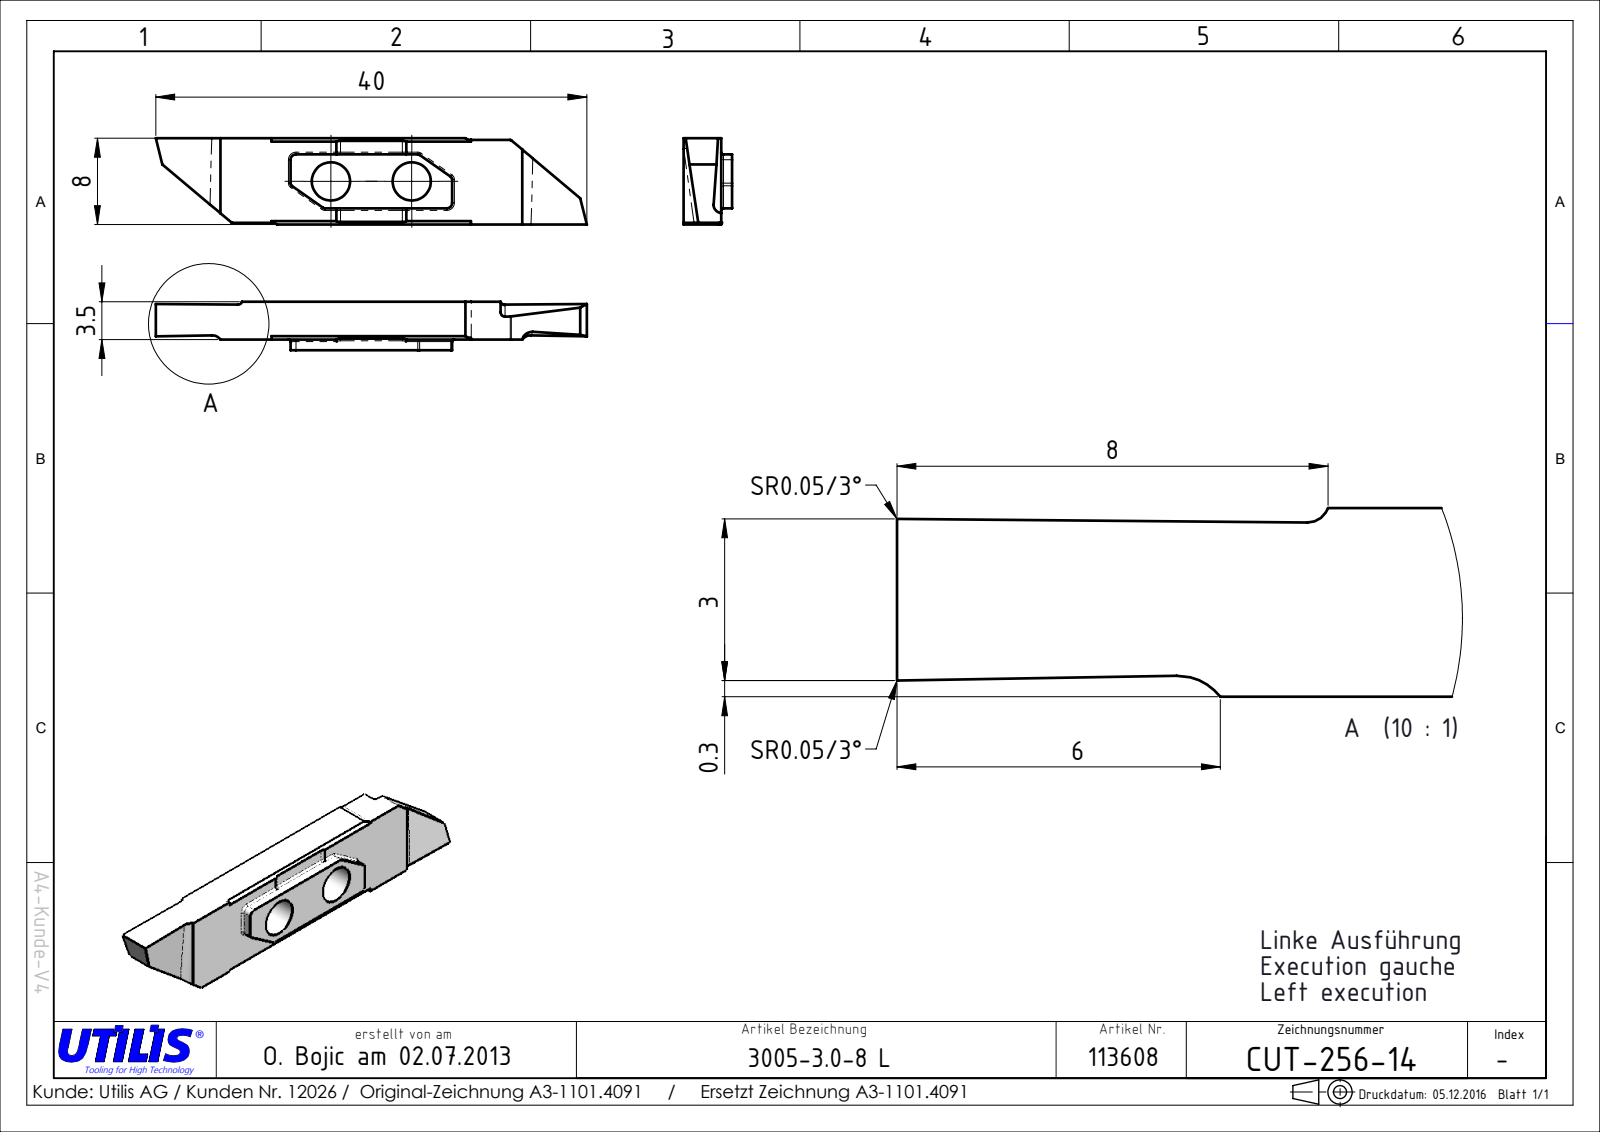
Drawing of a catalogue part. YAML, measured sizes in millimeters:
part_name: "CUT-256-14"
step_written_by: "SolidWorks 2016 (AUTOMOTIVE_DESIGN)"
units: millimeters
bodies: {solids: 1, faces: 36, planar: 22, cylindrical: 14, other: 0}
overall_size: [40, 8, 3.5]
volume: 853
surface_area: 874
round_holes:
  - {diameter: 3.55, count: 2}
partial_cylinders:
  - {radius: 0.15, count: 4}
  - {radius: 1, count: 4}
  - {radius: 0.4, count: 2}
face_to_face_distances: [3.5, 8, 22.54, 7.85, 7.7, 40, 38.98, 10.75, 29.25, 18.5]
hole_center_spacings: [7.5]
